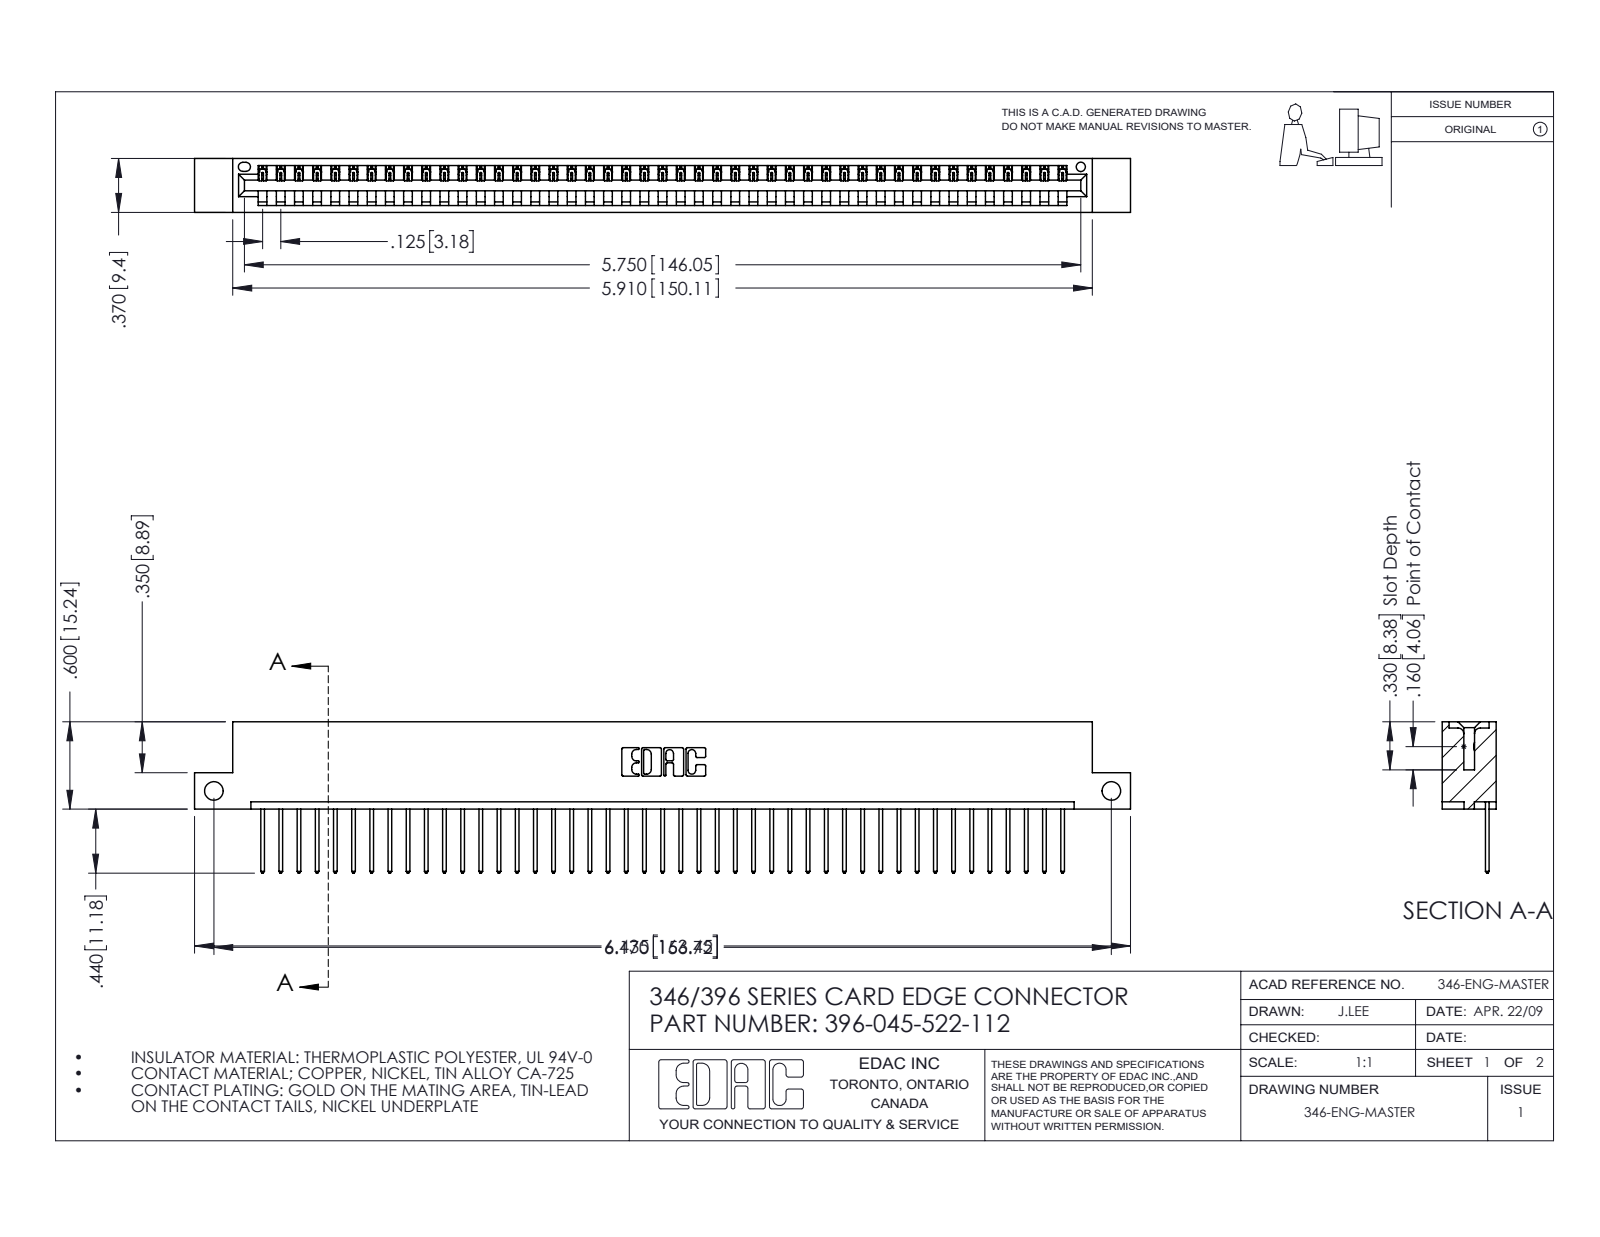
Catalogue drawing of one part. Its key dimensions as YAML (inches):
part_name: "346 Part_Flush Mounting Lugs - Side Mount; 345-292-001_345-293-122; 396-045-522-112"
step_written_by: "SolidWorks 2016 (CONFIG_CONTROL_DESIGN)"
units: inches
bodies: {solids: 46, faces: 2732, planar: 1876, cylindrical: 856, other: 0}
overall_size: [6.435, 1.04, 0.37]
volume: 0.951
surface_area: 30.27
round_holes:
  - {diameter: 0.128, count: 2}
  - {diameter: 0.064, count: 1}
partial_cylinders:
  - {radius: 0.006, count: 90}
  - {radius: 0.01, count: 90}
  - {radius: 0.01, count: 22}
  - {radius: 0.007, count: 6}
  - {radius: 0.031, count: 6}
  - {radius: 0.026, count: 3}
  - {radius: 0.031, count: 2}
  - {radius: 0.04, count: 2}
face_to_face_distances: [0.048, 0.322, 0.37, 0.25, 0.072, 0.298, 0.025, 0.148, 0.222, 0.1]
hole_center_spacings: [6.17]
